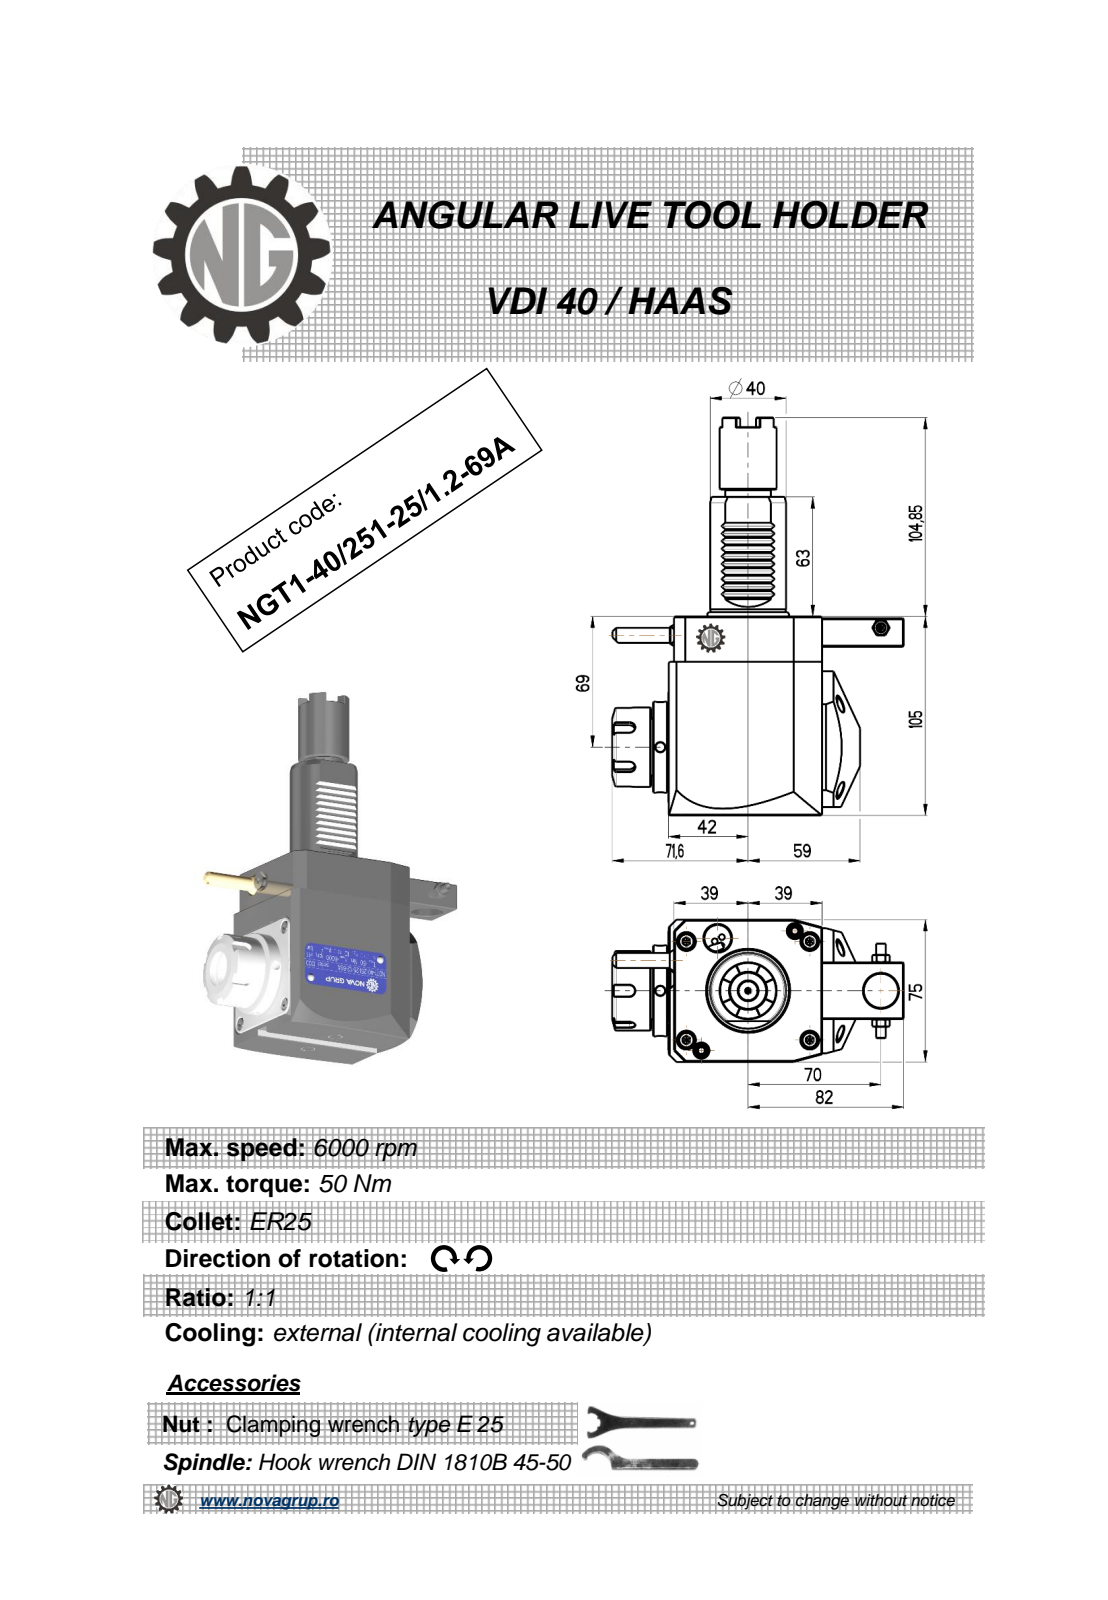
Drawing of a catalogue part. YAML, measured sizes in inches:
part_name: "NGT1_40_251_25_1_2_69A"
step_written_by: "PRO/ENGINEER BY PARAMETRIC TECHNOLOGY CORPORATION, 2010280 (CONFIG_CONTROL_DESIGN)"
units: inches
bodies: {solids: 1, faces: 476, planar: 223, cylindrical: 94, other: 159}
overall_size: [8.262, 6.047, 3.016]
volume: 50.68
surface_area: 111.7
round_holes:
  - {diameter: 0.197, count: 3}
  - {diameter: 0.118, count: 1}
  - {diameter: 0.165, count: 1}
  - {diameter: 0.374, count: 1}
  - {diameter: 0.709, count: 1}
  - {diameter: 0.799, count: 1}
round_bosses_or_shafts:
  - {diameter: 1.89, count: 1}
  - {diameter: 1.654, count: 1}
  - {diameter: 1.575, count: 1}
  - {diameter: 1.476, count: 1}
  - {diameter: 1.299, count: 1}
  - {diameter: 1.181, count: 1}
  - {diameter: 0.945, count: 1}
  - {diameter: 0.394, count: 1}
partial_cylinders:
  - {radius: 0.01, count: 12}
  - {radius: 0.012, count: 10}
  - {radius: 0.008, count: 6}
  - {radius: 0.118, count: 5}
  - {radius: 0.02, count: 1}
  - {radius: 0.384, count: 1}
  - {radius: 1.575, count: 1}
face_to_face_distances: [2.953, 4.134, 3.189, 3.504, 3.181, 0.039, 0.118, 0.11, 3.071, 0.315]
hole_center_spacings: [0.637, 2.407, 2.421, 4.577, 5.206]
